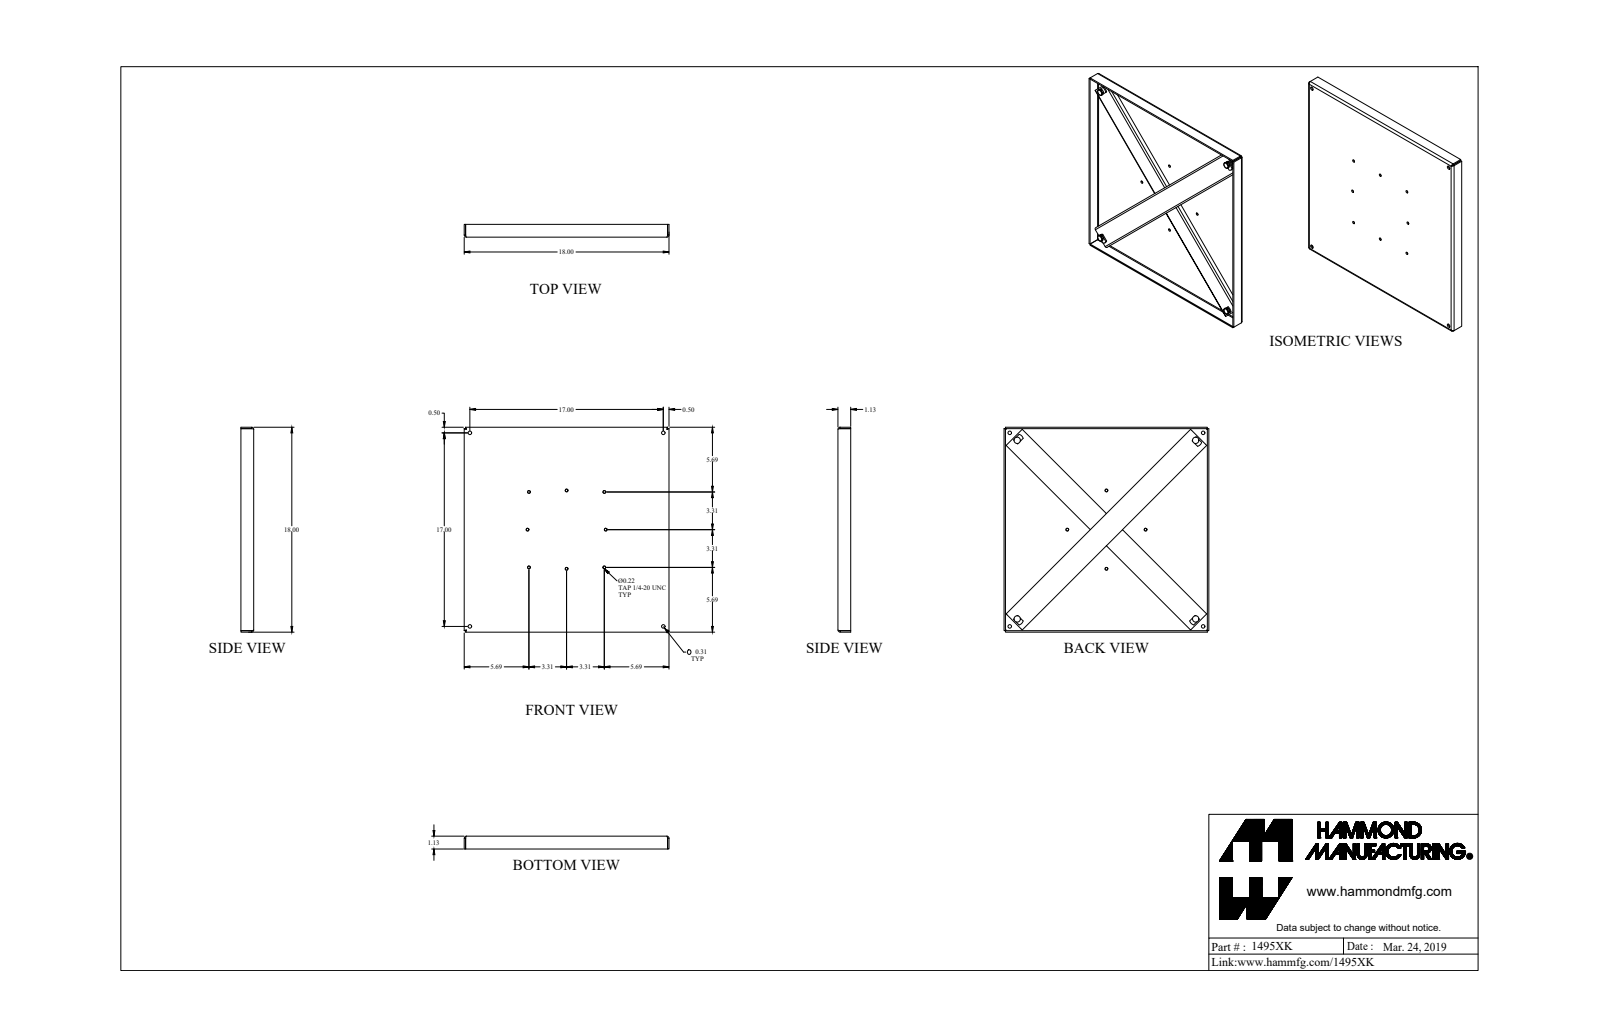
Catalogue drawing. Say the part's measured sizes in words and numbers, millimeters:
The part is named "1495XK_Default". Its 3-D file was written by "SolidWorks 2019 (CONFIG_CONTROL_DESIGN)". It is 23 solids with 374 faces: 137 planar, 106 cylindrical and 131 other. Overall it measures 457.2 by 457.2 by 31.4 millimeters. Its volume is 993 500 cubic millimeters and its surface area 680 000 square millimeters. Round holes: 8 of diameter 5.7, 8 of diameter 7.9, 5 of diameter 6.4, 4 of diameter 5.1. Round bosses or shafts: 5 of diameter 14.2, 5 of diameter 6.1, 4 of diameter 7.4. Partial cylindrical surfaces (rounded edges, fillets, slot ends): 8 of radius 12.7, 6 of radius 1.2, 6 of radius 3.6, 4 of radius 1.5, 4 of radius 4.7. The main face-to-face distances are 3.2, 12.7, 15.9, 2.4, 10.3, 13.5, 3.2, 454, 450.9, 457.2. The hole center spacings are 84.2, 191, 228.5, 251.3, 305.9, 327.7, 349, 372.2.
